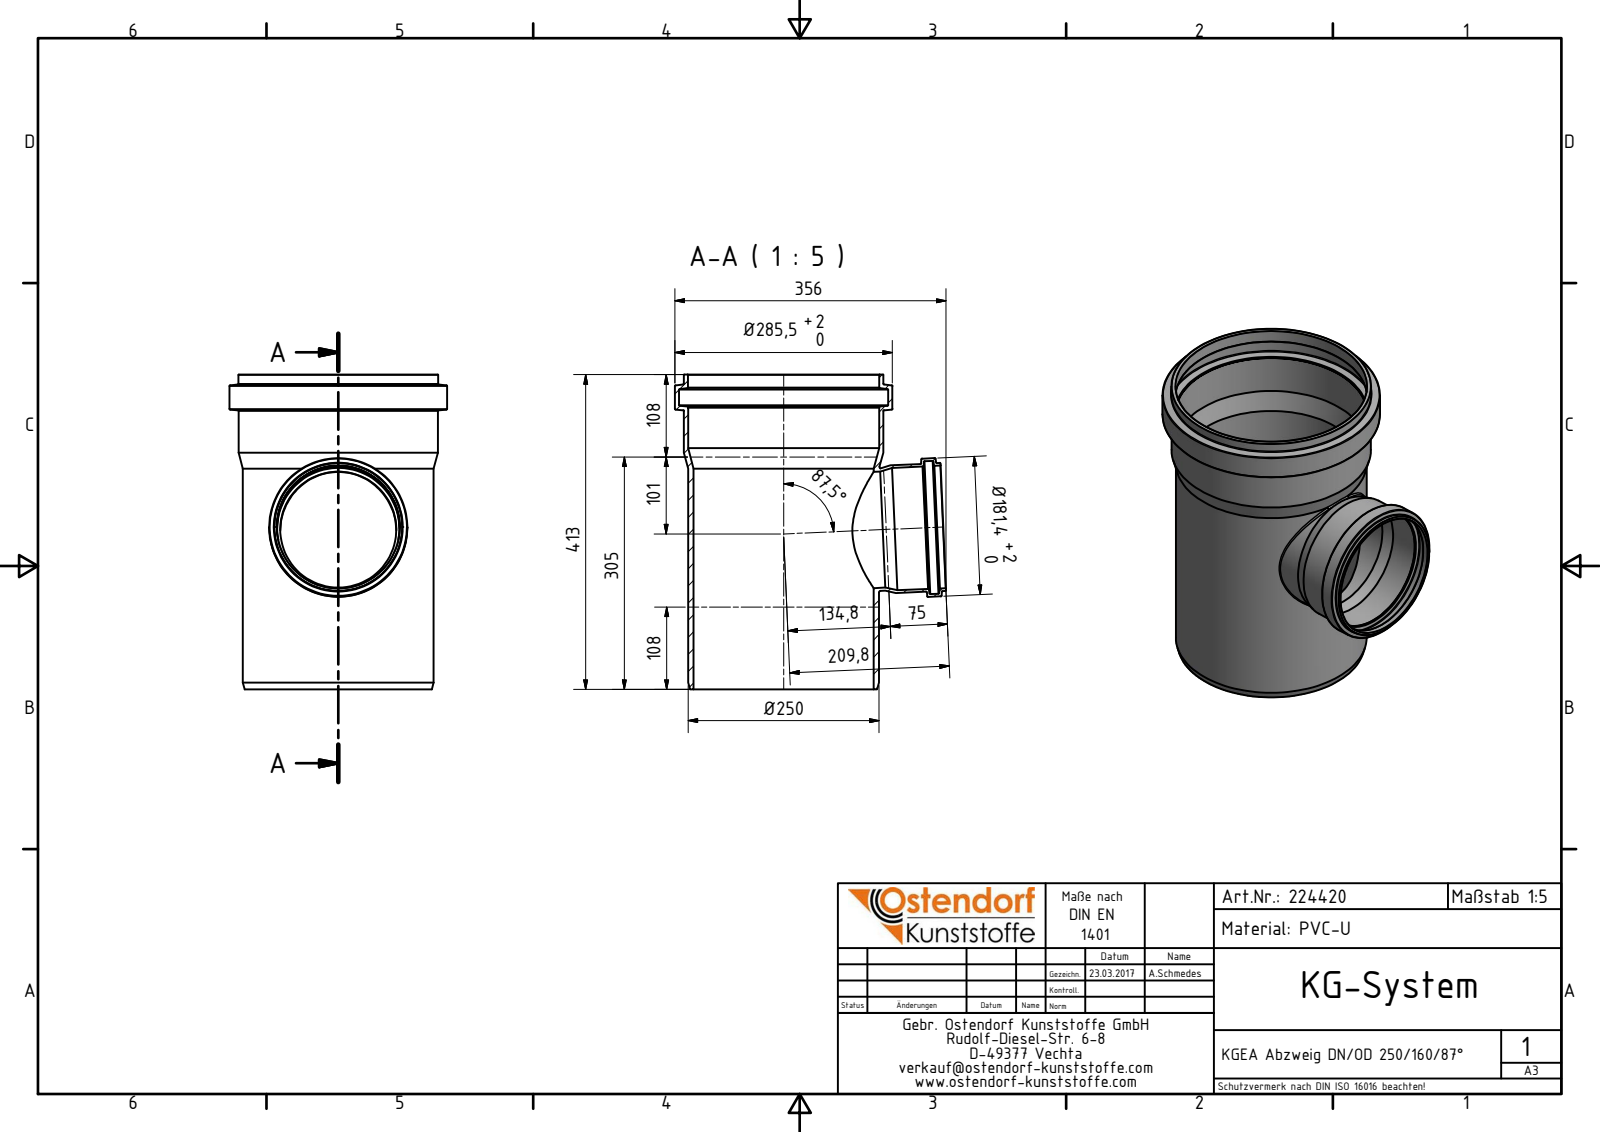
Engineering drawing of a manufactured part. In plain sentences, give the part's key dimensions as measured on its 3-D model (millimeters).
The part is named "224420 KGEA Abzweig DN_OD 250_160_87°". Its 3-D file was written by "Autodesk Inventor 2016 (AUTOMOTIVE_DESIGN)". It is 1 solid with 58 faces: 5 planar, 18 cylindrical and 35 other. Overall it measures 413 by 356 by 285.5 millimeters. Its volume is 2 319 000 cubic millimeters and its surface area 764 959 square millimeters. Round holes: 1 of diameter 152.3, 1 of diameter 160.7, 1 of diameter 161.1, 1 of diameter 174.4, 1 of diameter 236.3, 1 of diameter 250.8, 1 of diameter 251.1, 1 of diameter 274.5. Round bosses or shafts: 1 of diameter 285.5, 1 of diameter 262.1, 1 of diameter 261.8, 1 of diameter 250.5, 1 of diameter 181.4, 1 of diameter 168.1, 1 of diameter 167.7, 1 of diameter 160.3. The main face-to-face distances are 413, 369.77, 43.23, 23.61.
